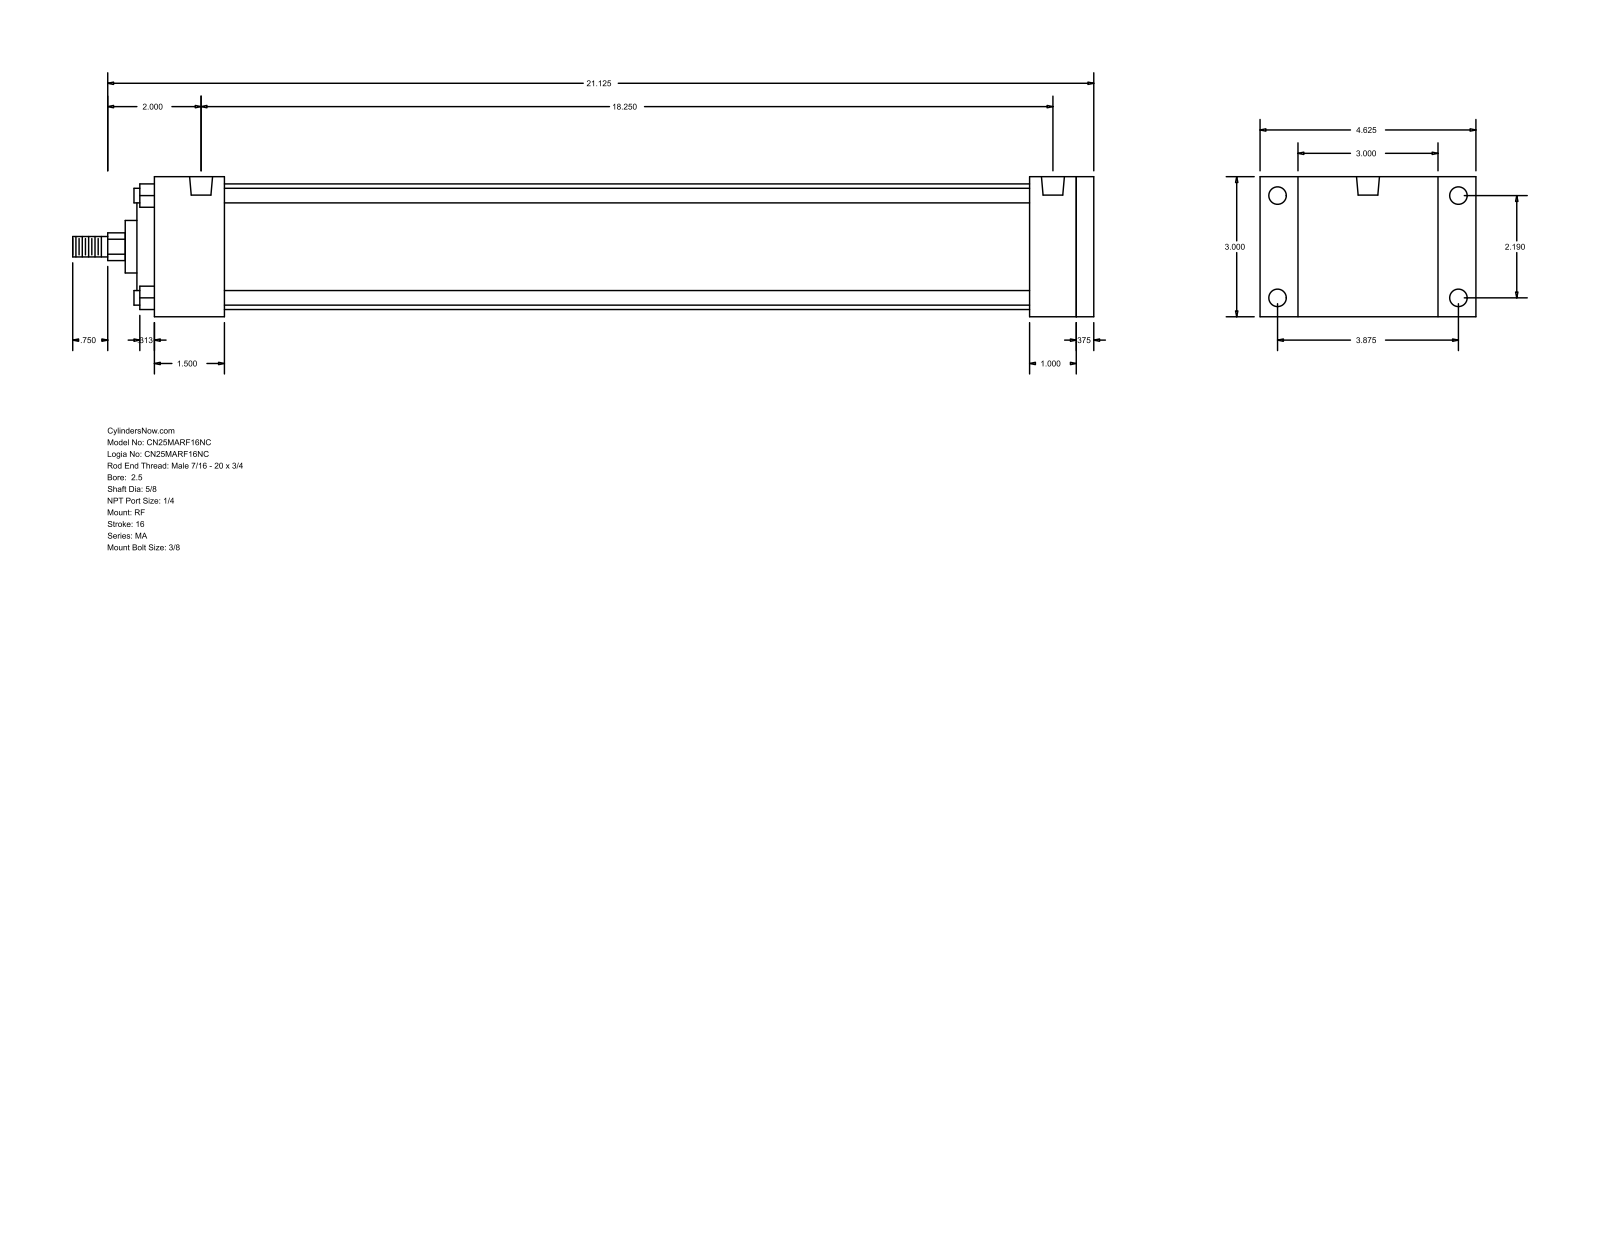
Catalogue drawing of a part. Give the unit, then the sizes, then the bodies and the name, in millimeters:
Units: millimetres
Overall size (bounding box): 555.62 × 117.47 × 76.2
Round holes (diameter × count): ⌀7.94 ×4, ⌀9.53 ×4, ⌀12.49 ×2
Round bosses / shafts (diameter × count): ⌀7.94 ×4, ⌀68.33 ×1, ⌀50.8 ×1, ⌀28.57 ×1, ⌀15.88 ×1, ⌀11.11 ×1
Partial cylindrical surfaces — rounded edges, fillets, slot ends (radius × count): R7.54 ×1
Main face-to-face distances: 76.2, 511.18, 9.53, 501.65, 25.4, 34.93, 38.1, 476.25, 438.15, 463.55
Hole centre spacings: 55.62, 98.42, 113.05, 463.55
Bodies: 0 solids, 94 faces (65 planar, 29 cylindrical, 0 other)
Part name (STEP PRODUCT): MA_RF__0250_0.625
STEP written by: GSSL Pune (CONFIG_CONTROL_DESIGN)
